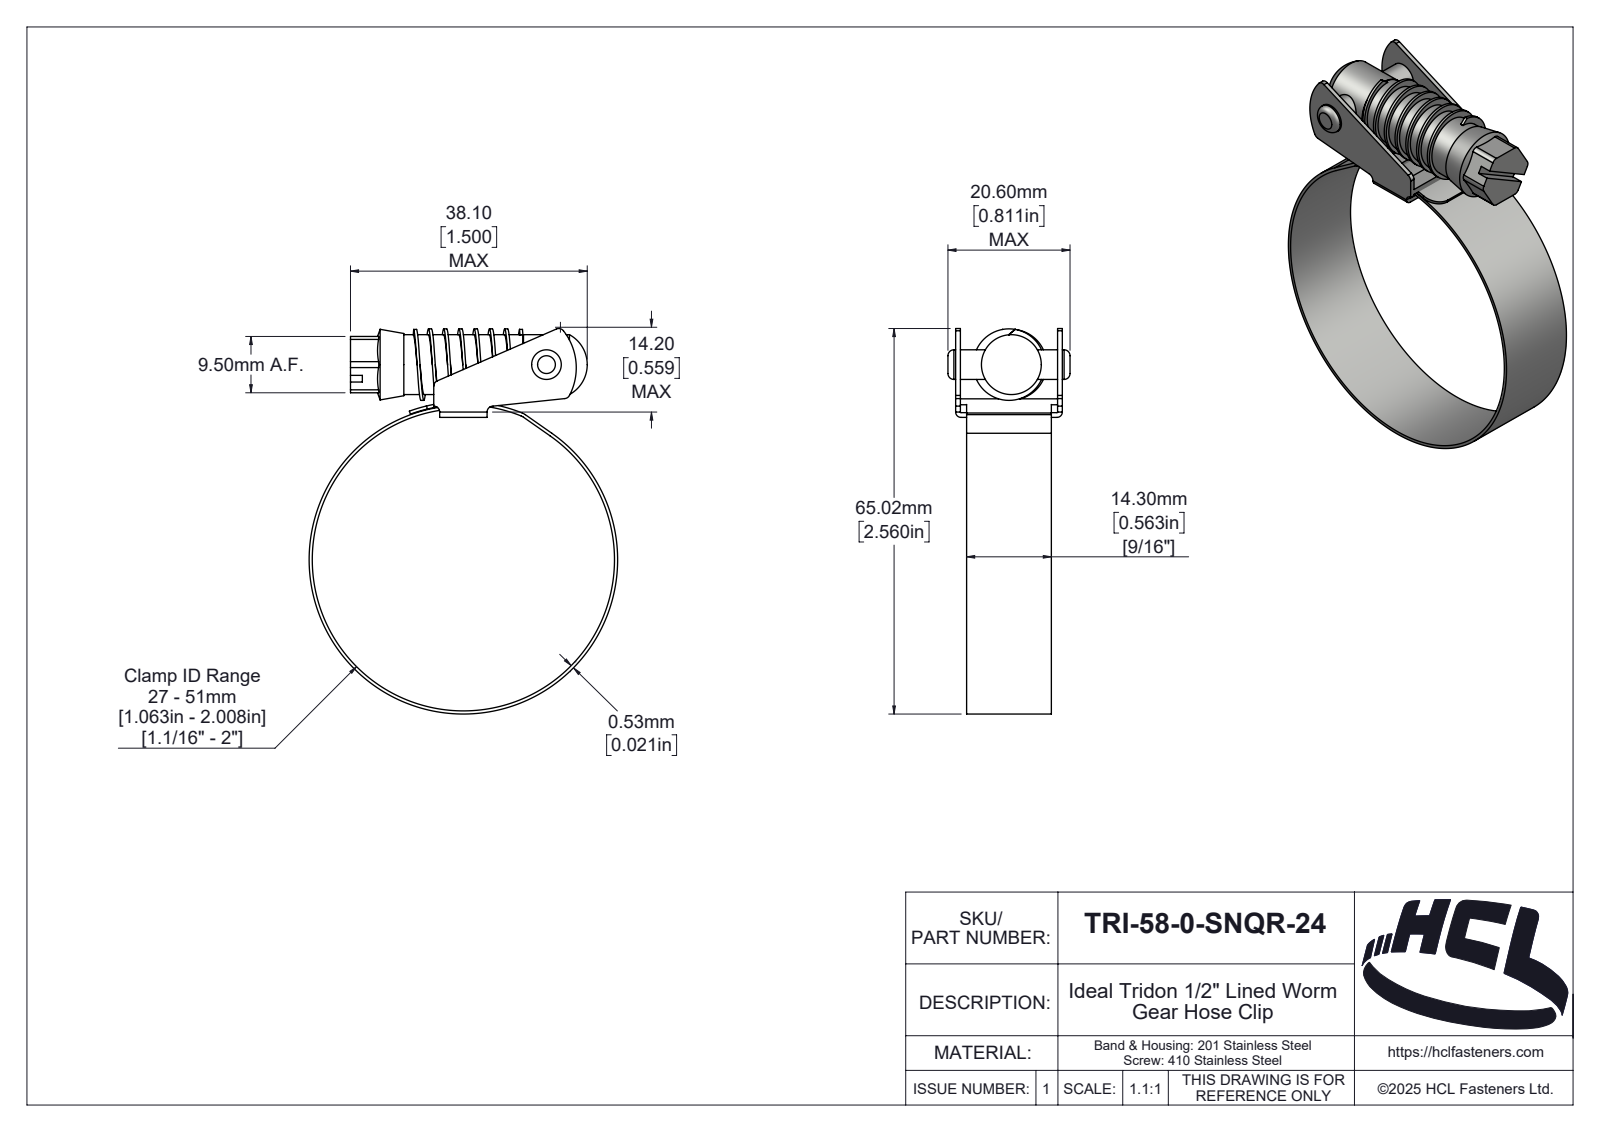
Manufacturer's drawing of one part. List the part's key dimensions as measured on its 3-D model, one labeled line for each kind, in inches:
Part name (STEP PRODUCT): TRI-58-0-SNQR-24
STEP written by: SolidWorks 2025 (AUTOMOTIVE_DESIGN)
Units: inches
Bodies: 5 solids, 222 faces (44 planar, 112 cylindrical, 66 other)
Overall size (bounding box): 2.56 × 2.05 × 0.811
Volume: 0.312 in³ · Surface area: 14 in²
Round holes (diameter × count): ⌀0.197 ×1, ⌀2.008 ×1
Round bosses / shafts (diameter × count): ⌀2.05 ×1, ⌀0.398 ×1
Partial cylindrical surfaces — rounded edges, fillets, slot ends (radius × count): R0.039 ×11, R0.004 ×2, R0.035 ×2, R0.118 ×2, R0.018 ×1, R0.074 ×1, R0.079 ×1, R0.093 ×1
Main face-to-face distances: 0.031, 0.677, 0.709, 0.646, 0.073, 0.636, 0.041, 0.604, 0.039, 0.084
Hole centre spacings: 1.408
